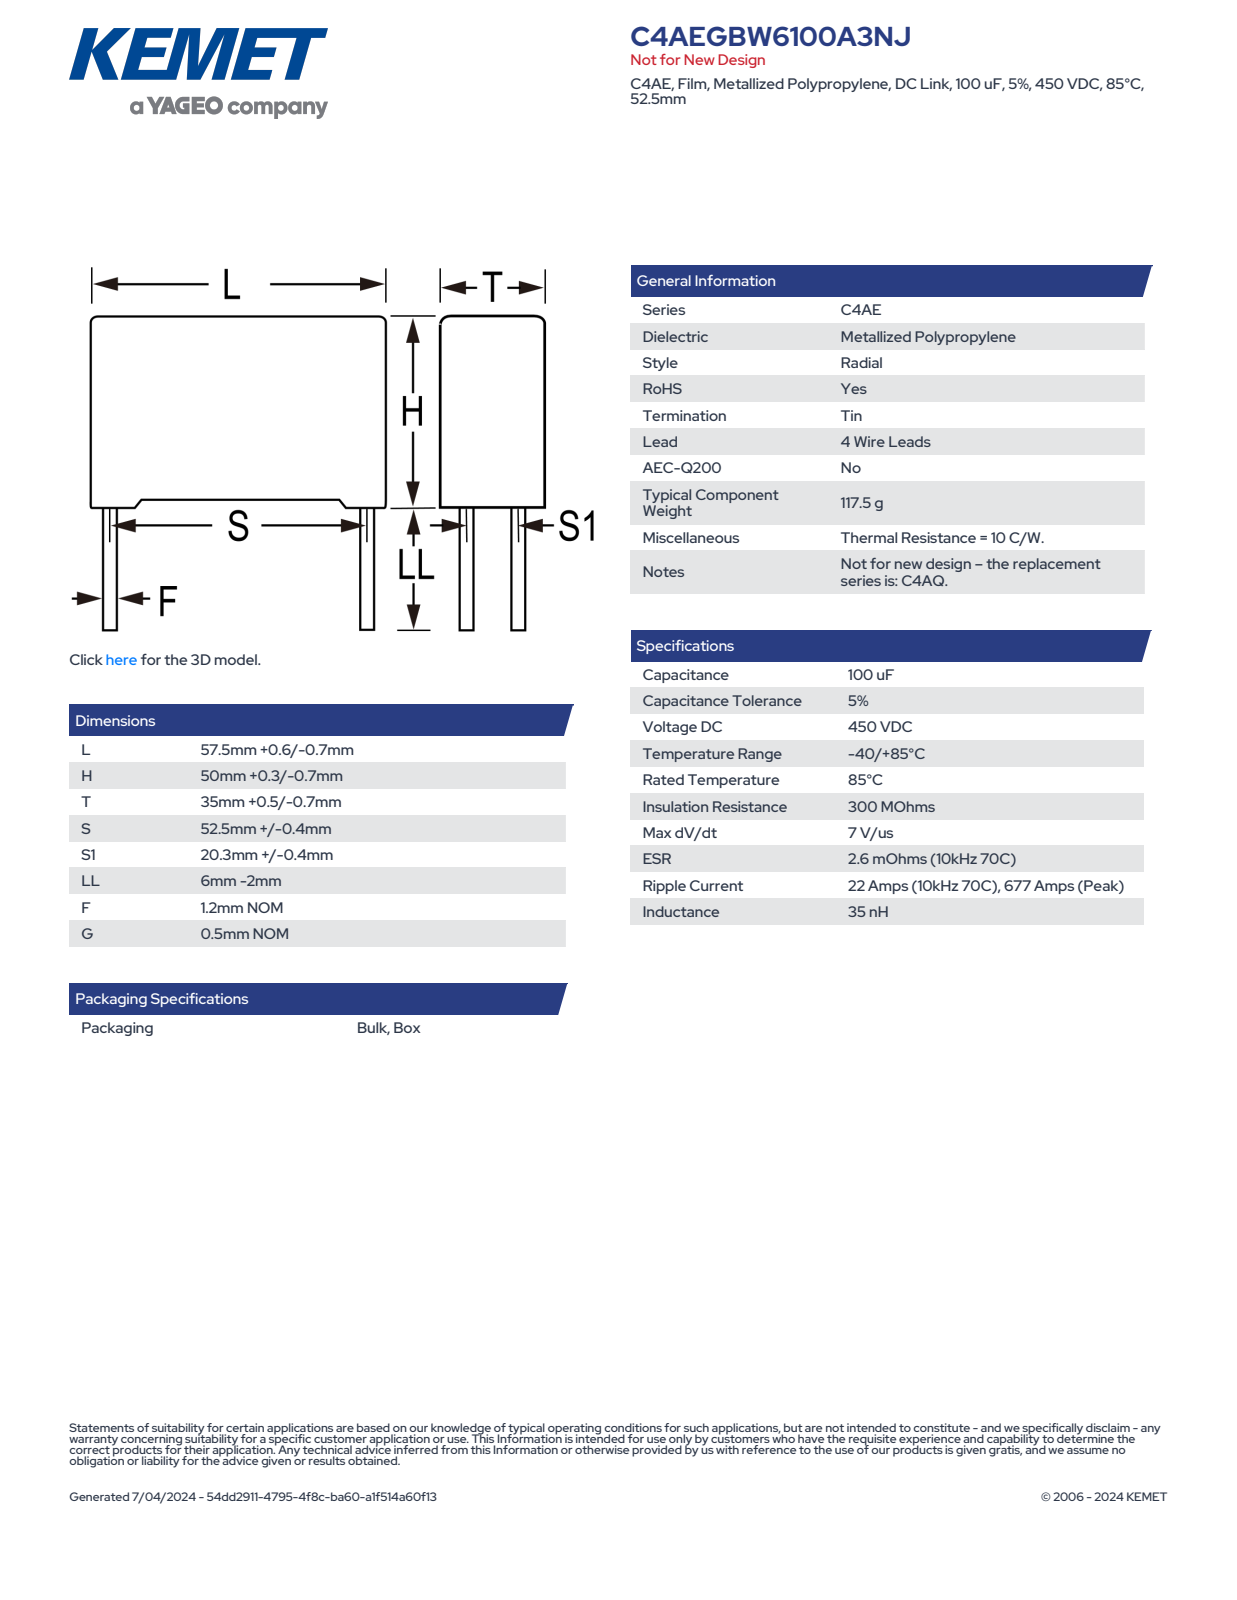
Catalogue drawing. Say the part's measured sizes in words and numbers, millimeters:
The part is named "CFP_RB4_57.5X50X35_L58.1H50.3T35.5S52.5S120.3LL4F1.2". Its 3-D file was written by "SolidWorks 2014 (AUTOMOTIVE_DESIGN)". It is 4 solids with 87 faces: 79 planar, 8 cylindrical and 0 other. Overall it measures 58.1 by 54.3 by 35.51 millimeters. Its volume is 101 021 cubic millimeters and its surface area 13 847 square millimeters. Round bosses or shafts: 4 of diameter 1.2. The main face-to-face distances are 35.5, 48.82, 58.1, 1.48, 50.3, 2.18, 55.92, 53.74, 33.32, 31.14.
